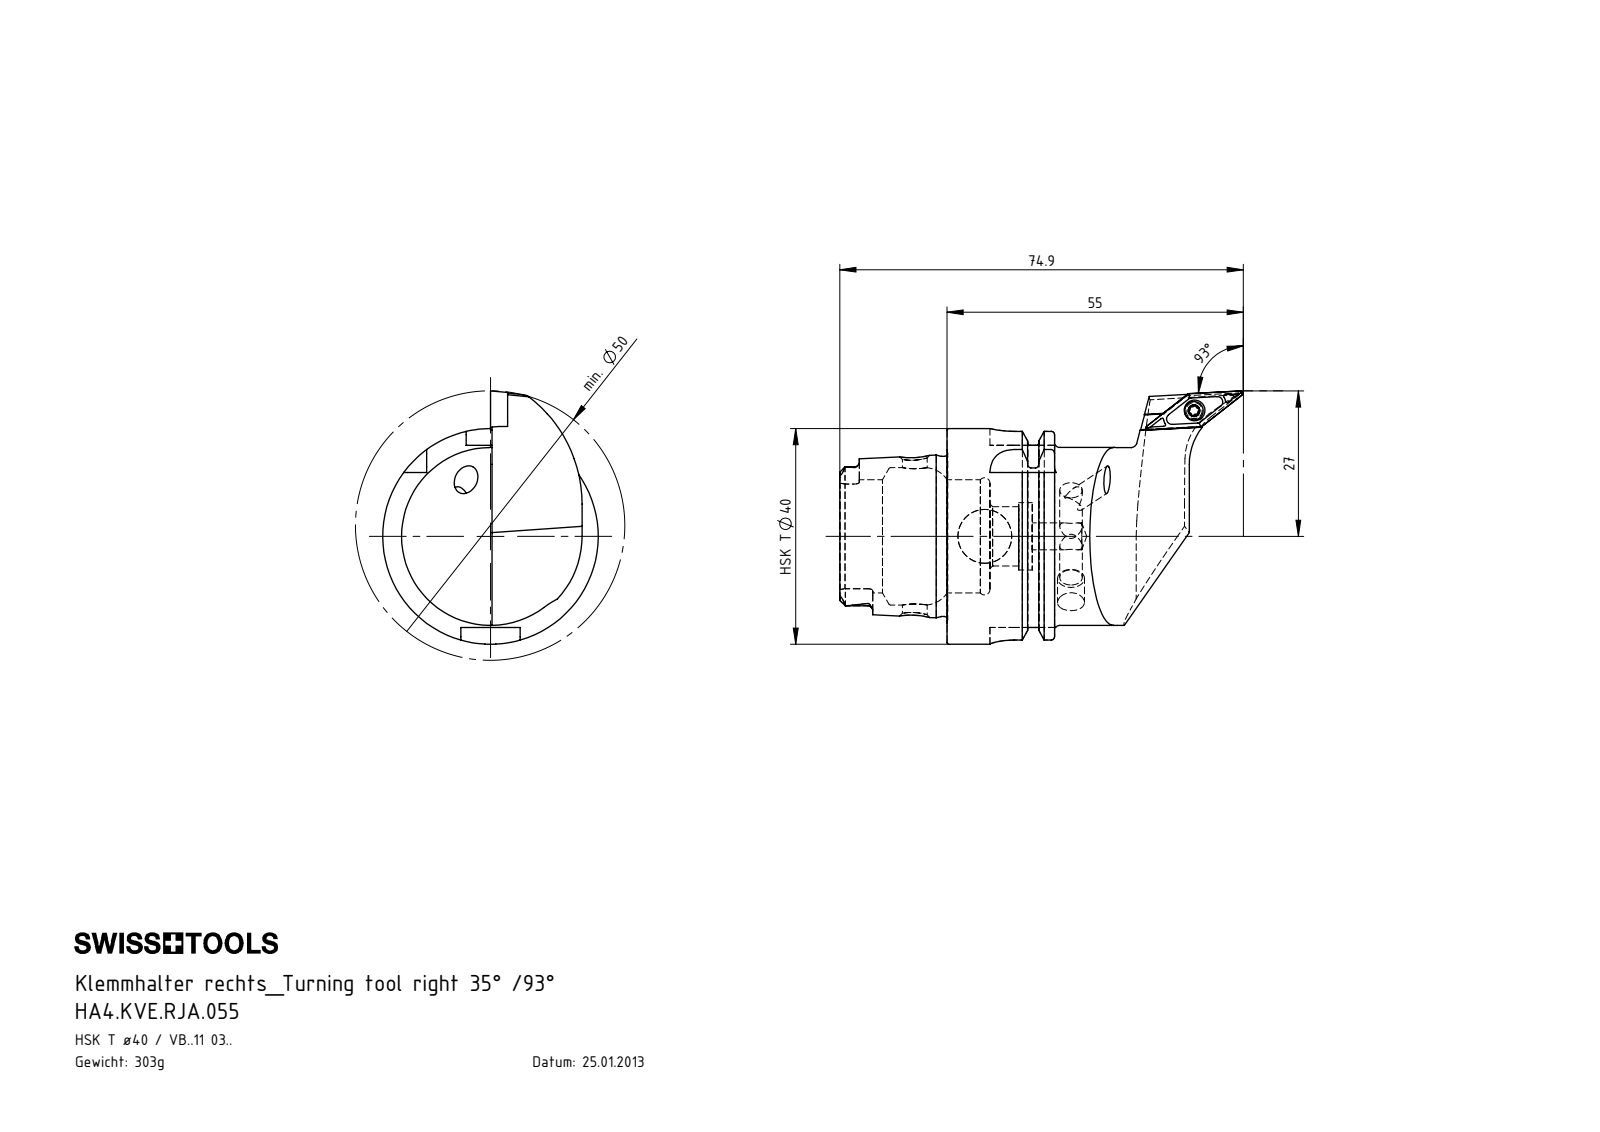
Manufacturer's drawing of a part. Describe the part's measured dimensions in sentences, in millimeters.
The part is named "HA4.KVE.RJA.055; WCA-ER2.001.006_A; KVT_MB_600_050; VBMT110304 (+1 more)". Its 3-D file was written by "SolidWorks 2017 (AUTOMOTIVE_DESIGN)". It is 5 solids with 239 faces: 83 planar, 62 cylindrical and 94 other. Overall it measures 74.9 by 47 by 40 millimeters. Its volume is 38 439 cubic millimeters and its surface area 13 115 square millimeters. Round holes: 2 of diameter 4.2, 2 of diameter 5, 1 of diameter 2.05, 1 of diameter 2.8, 1 of diameter 3.85, 1 of diameter 4, 1 of diameter 4.6, 1 of diameter 10, 1 of diameter 11, 1 of diameter 12.5, 1 of diameter 21, 1 of diameter 25.5. Round bosses or shafts: 1 of diameter 40, 1 of diameter 34.75, 1 of diameter 33, 1 of diameter 29.71, 1 of diameter 5, 1 of diameter 3.4, 1 of diameter 2.5. Partial cylindrical surfaces (rounded edges, fillets, slot ends): 6 of radius 0.21, 6 of radius 0.9, 5 of radius 0.36, 4 of radius 1.88, 4 of radius 4.5, 1 of radius 0.36, 1 of radius 0.8, 1 of radius 11. The main face-to-face distances are 7.95, 19.95, 12, 19.9, 27.85, 39.85, 2.88, 35.7, 15.8, 7.85. The hole center spacings are 45.31, 45.43.
